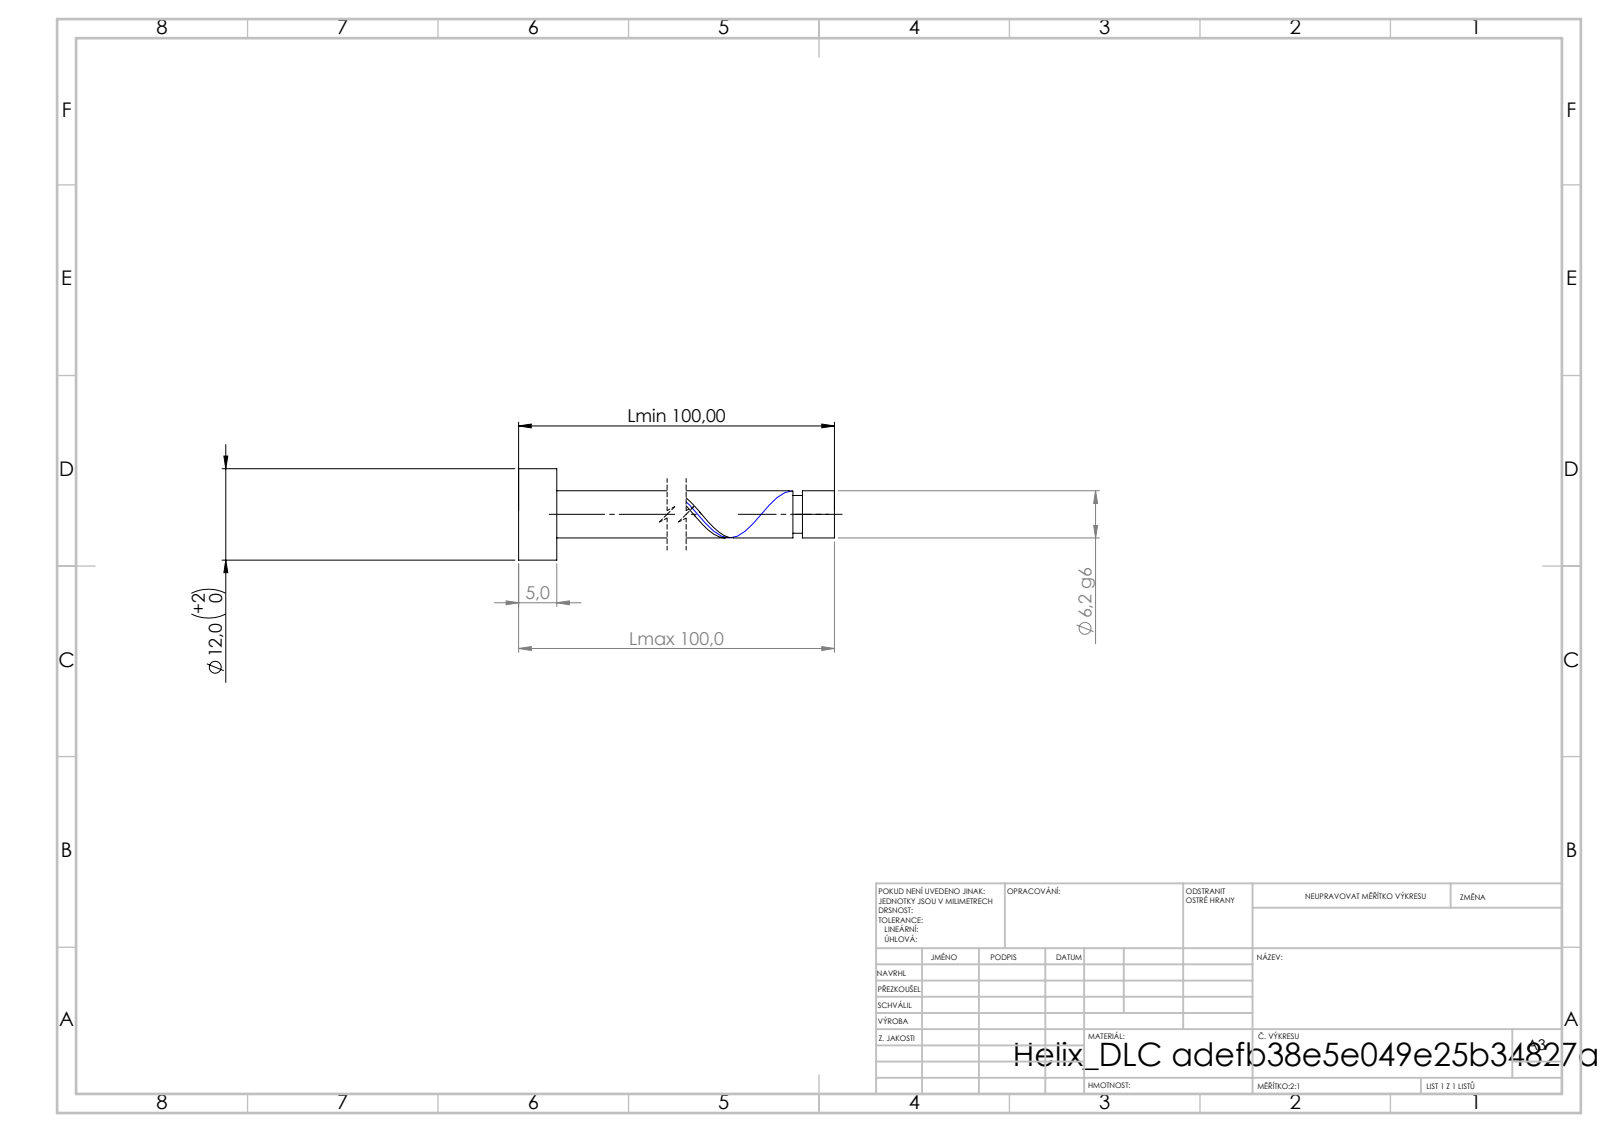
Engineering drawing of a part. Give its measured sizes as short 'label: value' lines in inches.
written by: SolidWorks 2019 (CONFIG_CONTROL_DESIGN)
unit: in
bodies: 1 solid, 21 faces (6 planar, 14 cylindrical, 1 other)
size: 3.937 × 0.472 × 0.472
volume: 0.207 in³; area: 3.619 in²
bosses: 1× ⌀0.472, 1× ⌀0.244, 1× ⌀0.195
face distances: 0.197, 3.937, 3.74, 3.771, 3.574, 0.166, 3.722, 3.526, 0.049, 0.215
